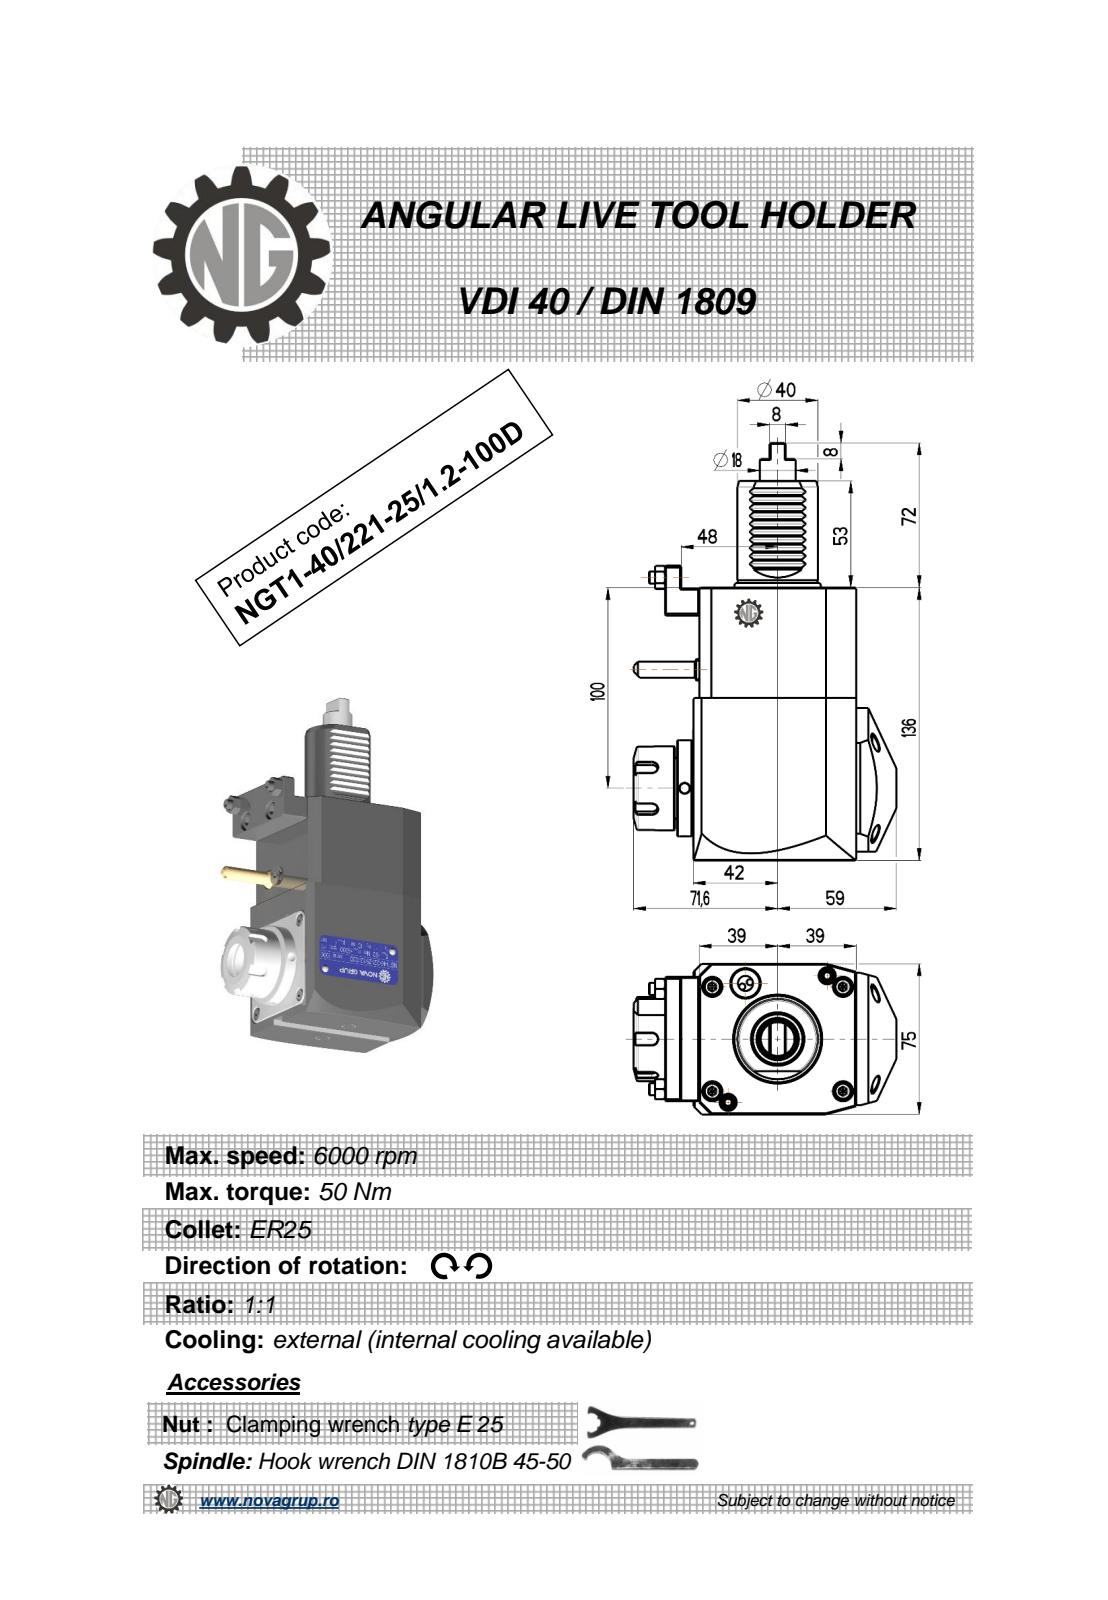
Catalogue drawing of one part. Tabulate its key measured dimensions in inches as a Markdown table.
| quantity | value |
| --- | --- |
| part name | NGT1_40_221_25_1_2_100D |
| STEP written by | PRO/ENGINEER BY PARAMETRIC TECHNOLOGY CORPORATION, 2010280 (CONFIG_CONTROL_DESIGN) |
| units | inches |
| bodies | 1 solid, 406 faces (174 planar, 77 cylindrical, 155 other) |
| overall size | 8.189 × 5.142 × 3.016 |
| volume | 59.85 in³ |
| surface area | 118 in² |
| round holes (diameter × count) | 0.197 × 3, 0.118 × 1, 0.799 × 1 |
| round bosses / shafts (diameter × count) | 0.236 × 2, 1.89 × 1, 1.654 × 1, 1.575 × 1, 1.476 × 1, 1.299 × 1, 0.701 × 1, 0.441 × 1 |
| partial cylindrical surfaces (radius × count) | 0.012 × 10, 0.012 × 10, 0.009 × 6, 0.118 × 5, 0.031 × 2, 0.02 × 1, 1.575 × 1 |
| main face-to-face distances | 2.953, 5.354, 3.189, 3.071, 0.551, 0.118, 0.315, 0.433, 0.02, 0.11 |
| hole center spacings | 2.407 |
